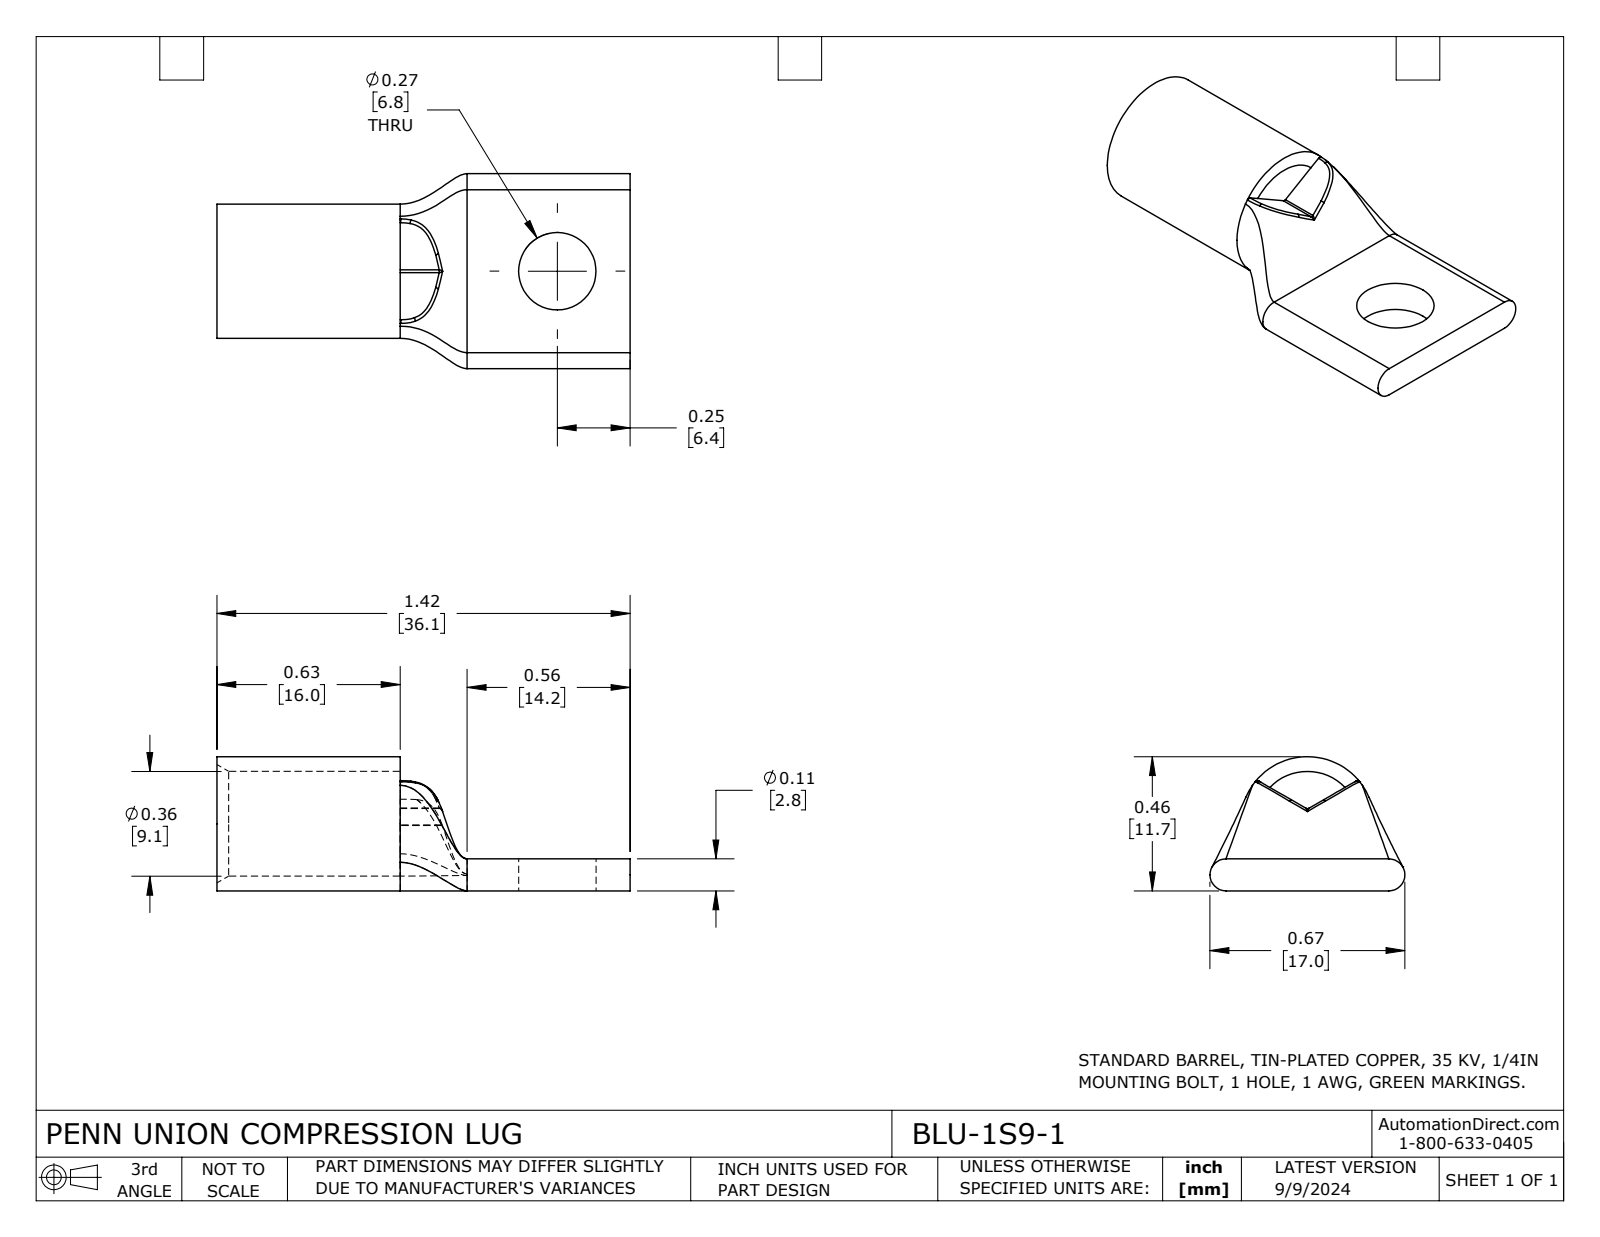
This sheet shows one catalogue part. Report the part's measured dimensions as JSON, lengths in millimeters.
{"part_name": "BLU-1S9-1", "step_written_by": "SolidWorks 2023 (CONFIG_CONTROL_DESIGN)", "units": "millimeters", "bodies": {"solids": 1, "faces": 41, "planar": 11, "cylindrical": 11, "other": 19}, "overall_size": [36.1, 17, 11.7], "volume_mm3": 1500, "surface_area_mm2": 2144, "round_holes": [[6.8, 1], [9.1, 1]], "round_bosses_or_shafts": [[11.7, 1]], "partial_cylinders_radius": [[0.3, 2], [1.4, 2]], "face_to_face_distances": [2.8, 1.3, 36.1, 16, 20.1, 21.8, 5.8, 14.2]}
